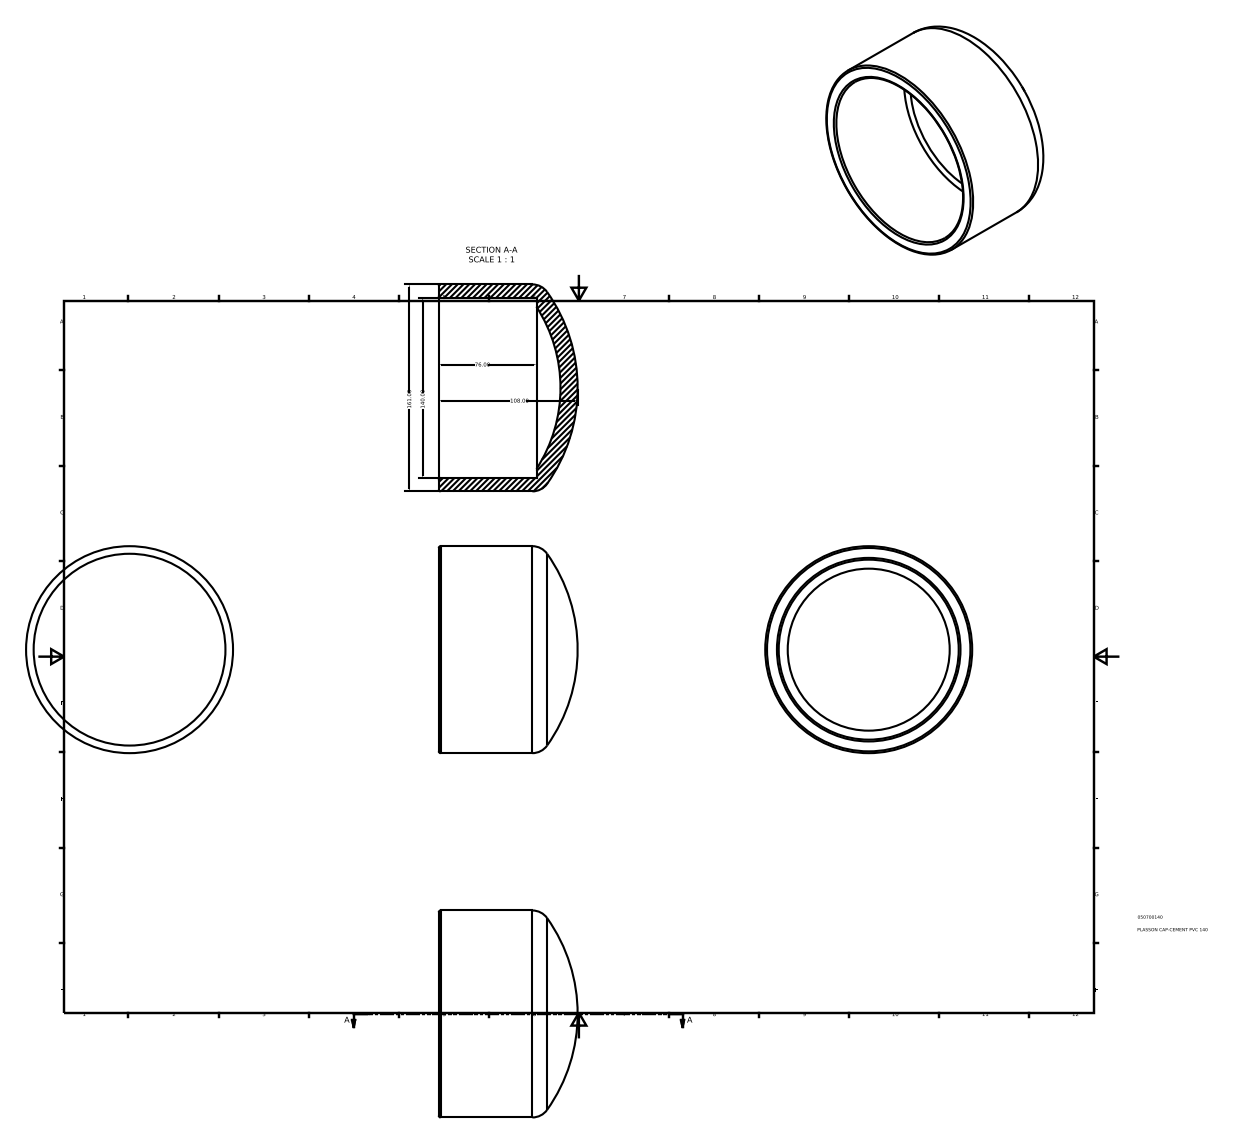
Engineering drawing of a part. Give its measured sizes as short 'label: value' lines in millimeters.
name: 050700140
written by: Autodesk Inventor 2015 (AUTOMOTIVE_DESIGN)
unit: mm
bodies: 1 solid, 9 faces (2 planar, 2 cylindrical, 5 other)
size: 161 × 161 × 108
volume: 629 649 mm³; area: 116 984 mm²
holes: 1× ⌀140
bosses: 1× ⌀161
face distances: 76
